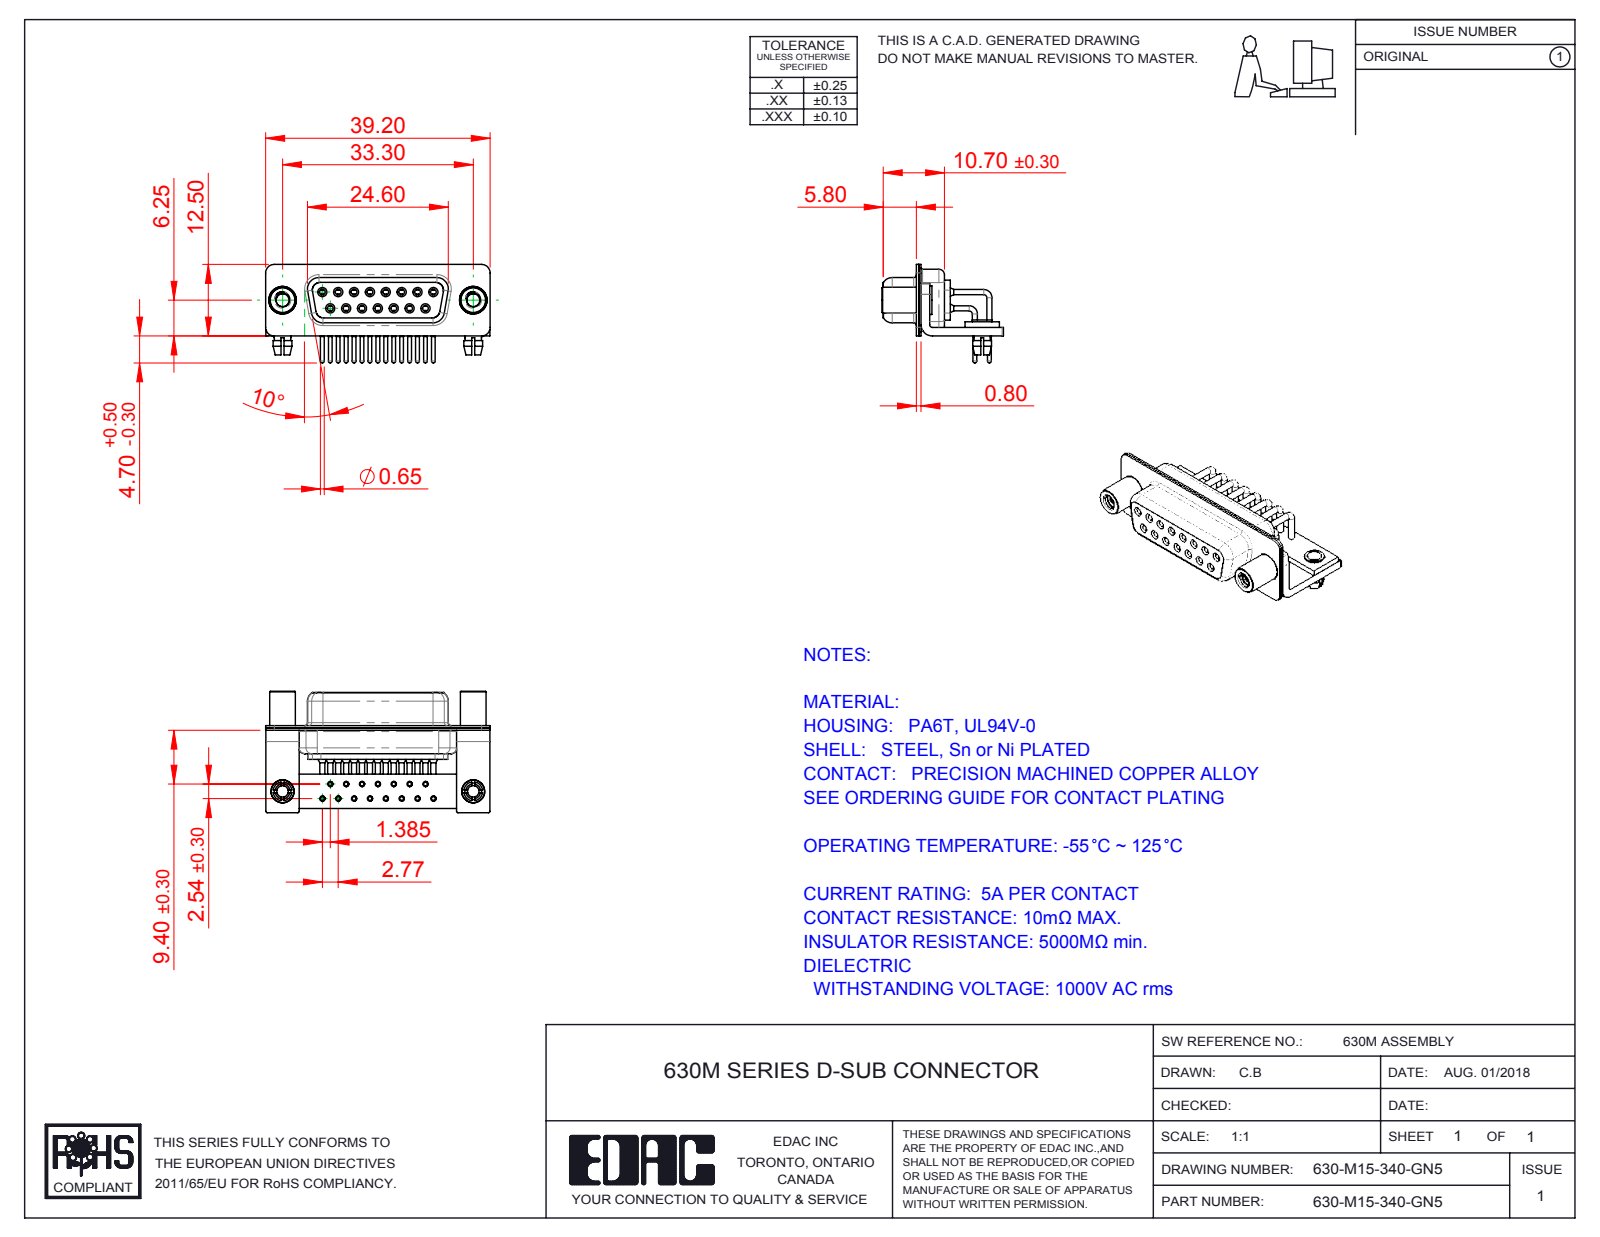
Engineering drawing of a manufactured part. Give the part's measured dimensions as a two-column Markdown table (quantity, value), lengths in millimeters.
| quantity | value |
| --- | --- |
| part name | 630M Contact Row 1; 630M Stabilizer Bracket; 630M Shell Front_15 Contacts; 630M Shell Rear_15 Contacts (+6 more) |
| STEP written by | SolidWorks 2016 (CONFIG_CONTROL_DESIGN) |
| units | millimeters |
| bodies | 25 solids, 1296 faces (368 planar, 608 cylindrical, 320 other) |
| overall size | 39.2 × 21.2 × 17.2 |
| volume | 3 217 mm³ |
| surface area | 8 278 mm² |
| round holes (diameter × count) | 2 × 17, 0.9 × 15, 1 × 15, 1.1 × 15, 1.7 × 15, 1.8 × 15, 2.26 × 2, 2.5 × 2, 3.2 × 2, 4 × 2, 4.8 × 2 |
| round bosses / shafts (diameter × count) | 0.9 × 27, 1.6 × 15, 1.5 × 15, 0.65 × 15, 5 × 2, 4.9 × 2, 4.5 × 2, 4 × 2 |
| partial cylindrical surfaces (radius × count) | 0.25 × 16, 1.5 × 16, 2 × 13, 1.35 × 8, 1.6 × 8, 0.5 × 5, 0.6 × 4, 0.65 × 4 |
| main face-to-face distances | 0.4, 2.3, 1.9, 0.8, 1.5, 9.35, 1, 1.45, 8.95, 0.85 |
| hole center spacings | 2.77, 5.54, 8.31, 3.16, 4.87, 11.08, 2.89, 7.37 |
